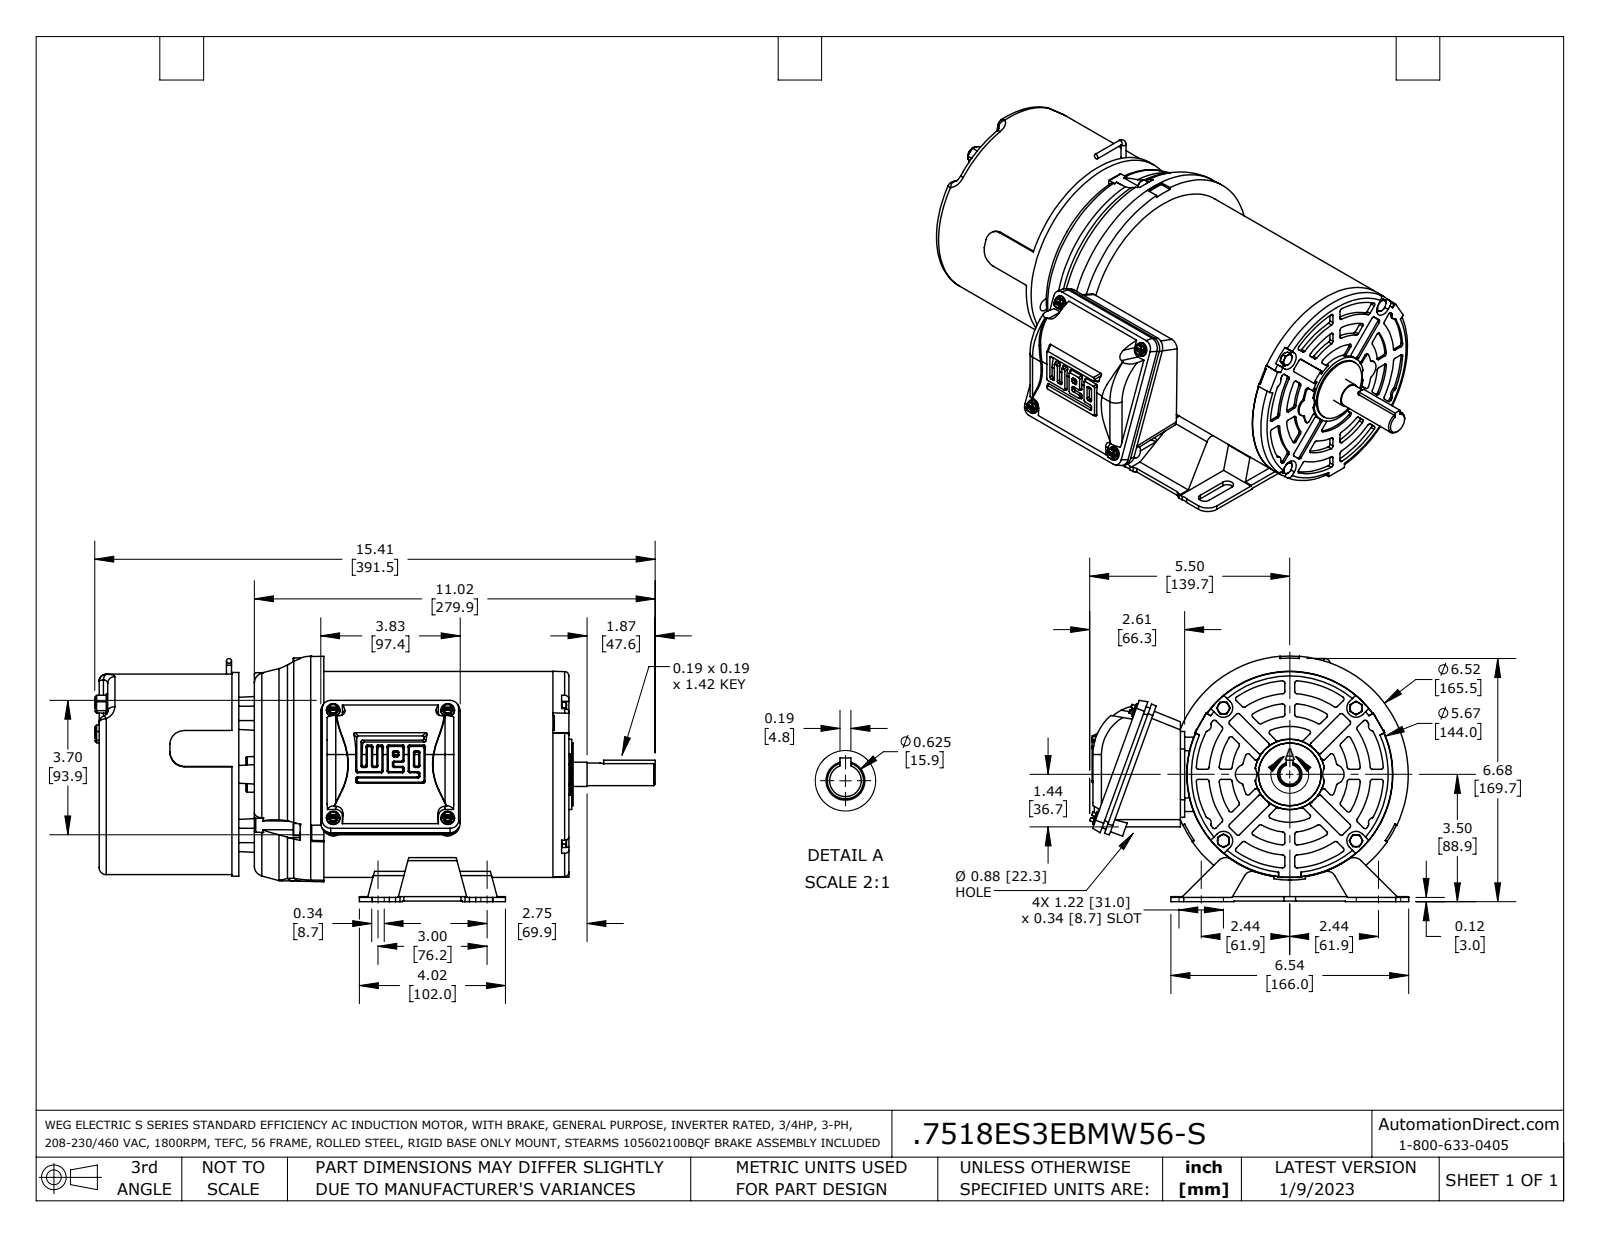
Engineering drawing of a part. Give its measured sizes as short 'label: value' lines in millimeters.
name: W56C_3PH_TEFC_BM_15398 coord fxt
written by: SolidWorks 2021 (AUTOMOTIVE_DESIGN)
unit: mm
bodies: 16 solids, 1498 faces (582 planar, 422 cylindrical, 494 other)
size: 391.4 × 222.7 × 171.5
volume: 5 331 000 mm³; area: 453 000 mm²
holes: 4× ⌀6, 2× ⌀6.4, 2× ⌀7.1, 2× ⌀9.4, 1× ⌀12.7, 1× ⌀76.2, 1× ⌀131
bosses: 4× ⌀9.5, 4× ⌀4.7, 3× ⌀8.5, 3× ⌀5, 2× ⌀14, 2× ⌀11.1, 2× ⌀3.5, 1× ⌀143.7
rounds: 92× R1.5, 38× R1.2, 15× R5, 10× R0.5, 8× R4.3, 8× R5.2, 8× R7, 4× R3.5
face distances: 160, 14.5, 174.5, 45, 201, 26.5, 41, 219.5, 18.5, 59.5
hole spacings: 80, 18.2, 47.6, 56.6, 59.4, 80, 106.1, 113.1
